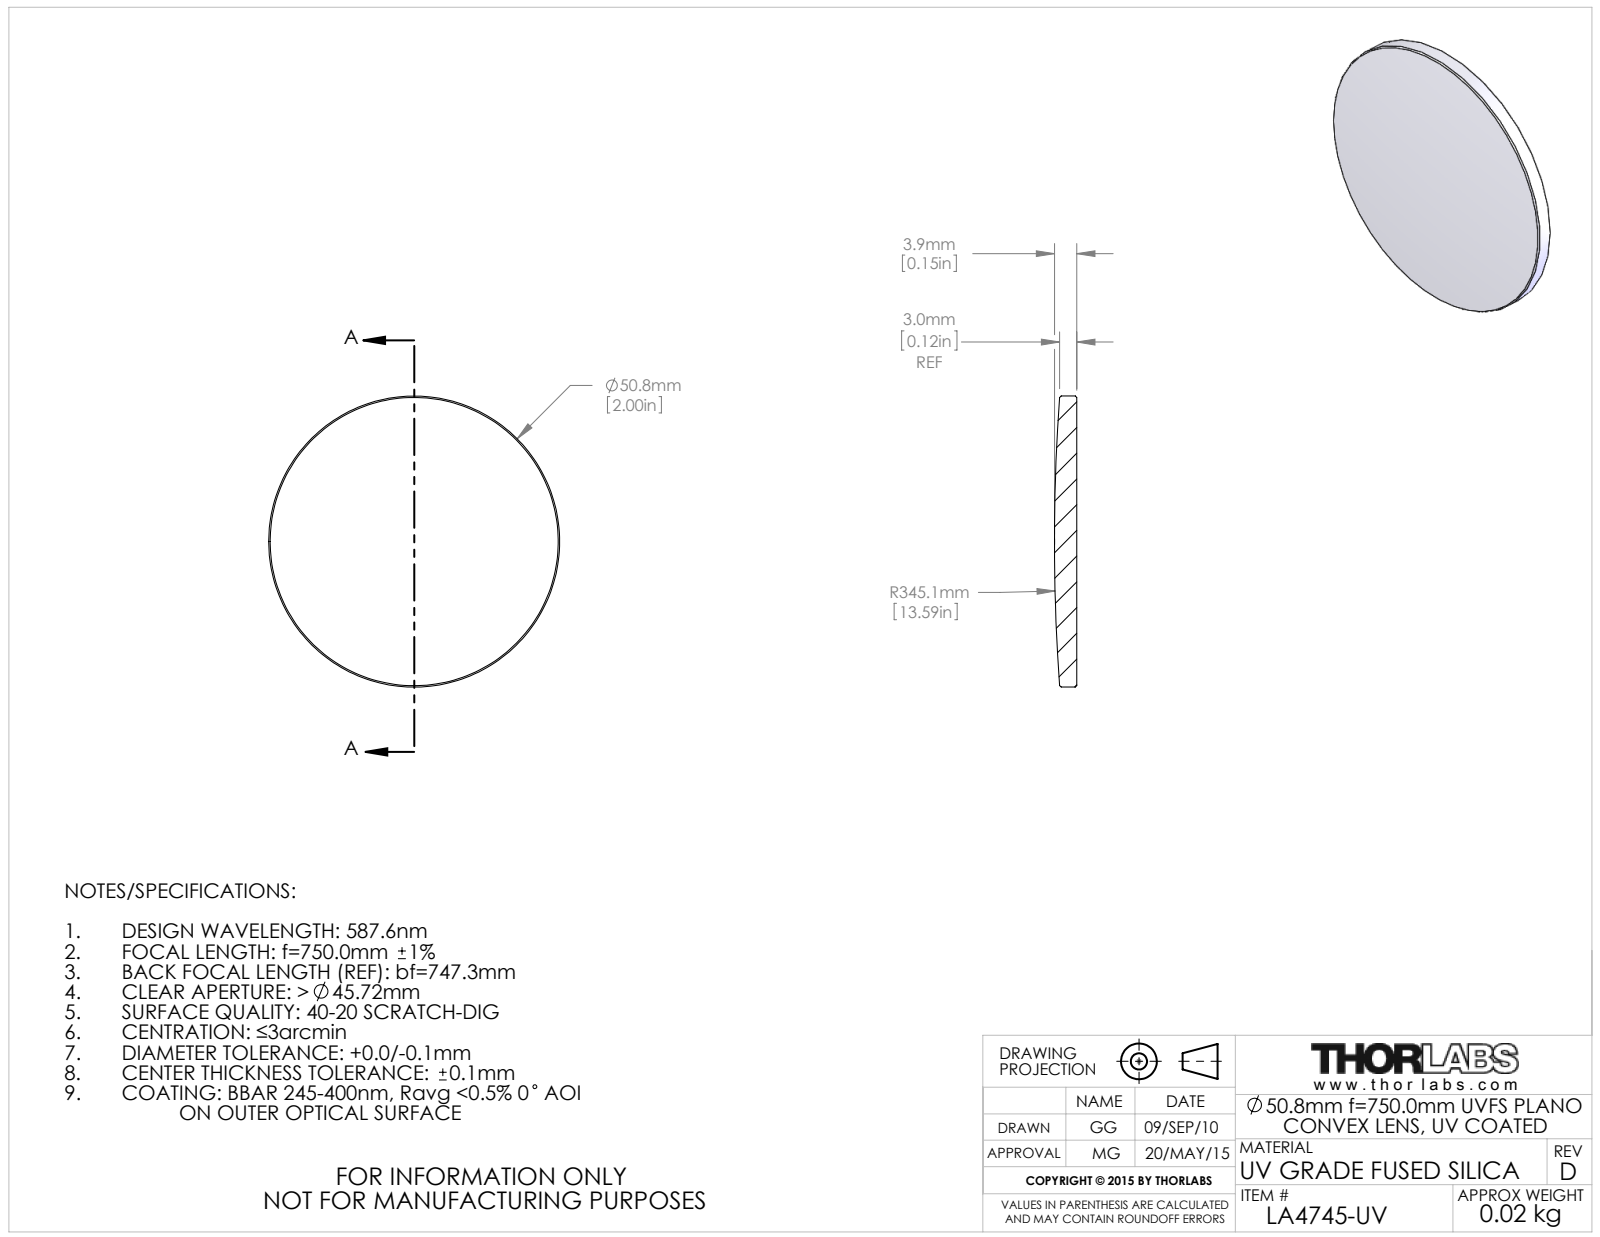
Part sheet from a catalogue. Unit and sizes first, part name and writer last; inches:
Units: inches
Overall size (bounding box): 2 × 2 × 0.154
Round bosses / shafts (diameter × count): ⌀2 ×1
Volume: 0.427 in³ · Surface area: 6.958 in²
Bodies: 1 solid, 9 faces (1 planar, 2 cylindrical, 6 other)
Part name (STEP PRODUCT): 4300-E0W
STEP written by: SolidWorks 2014 (CONFIG_CONTROL_DESIGN)
